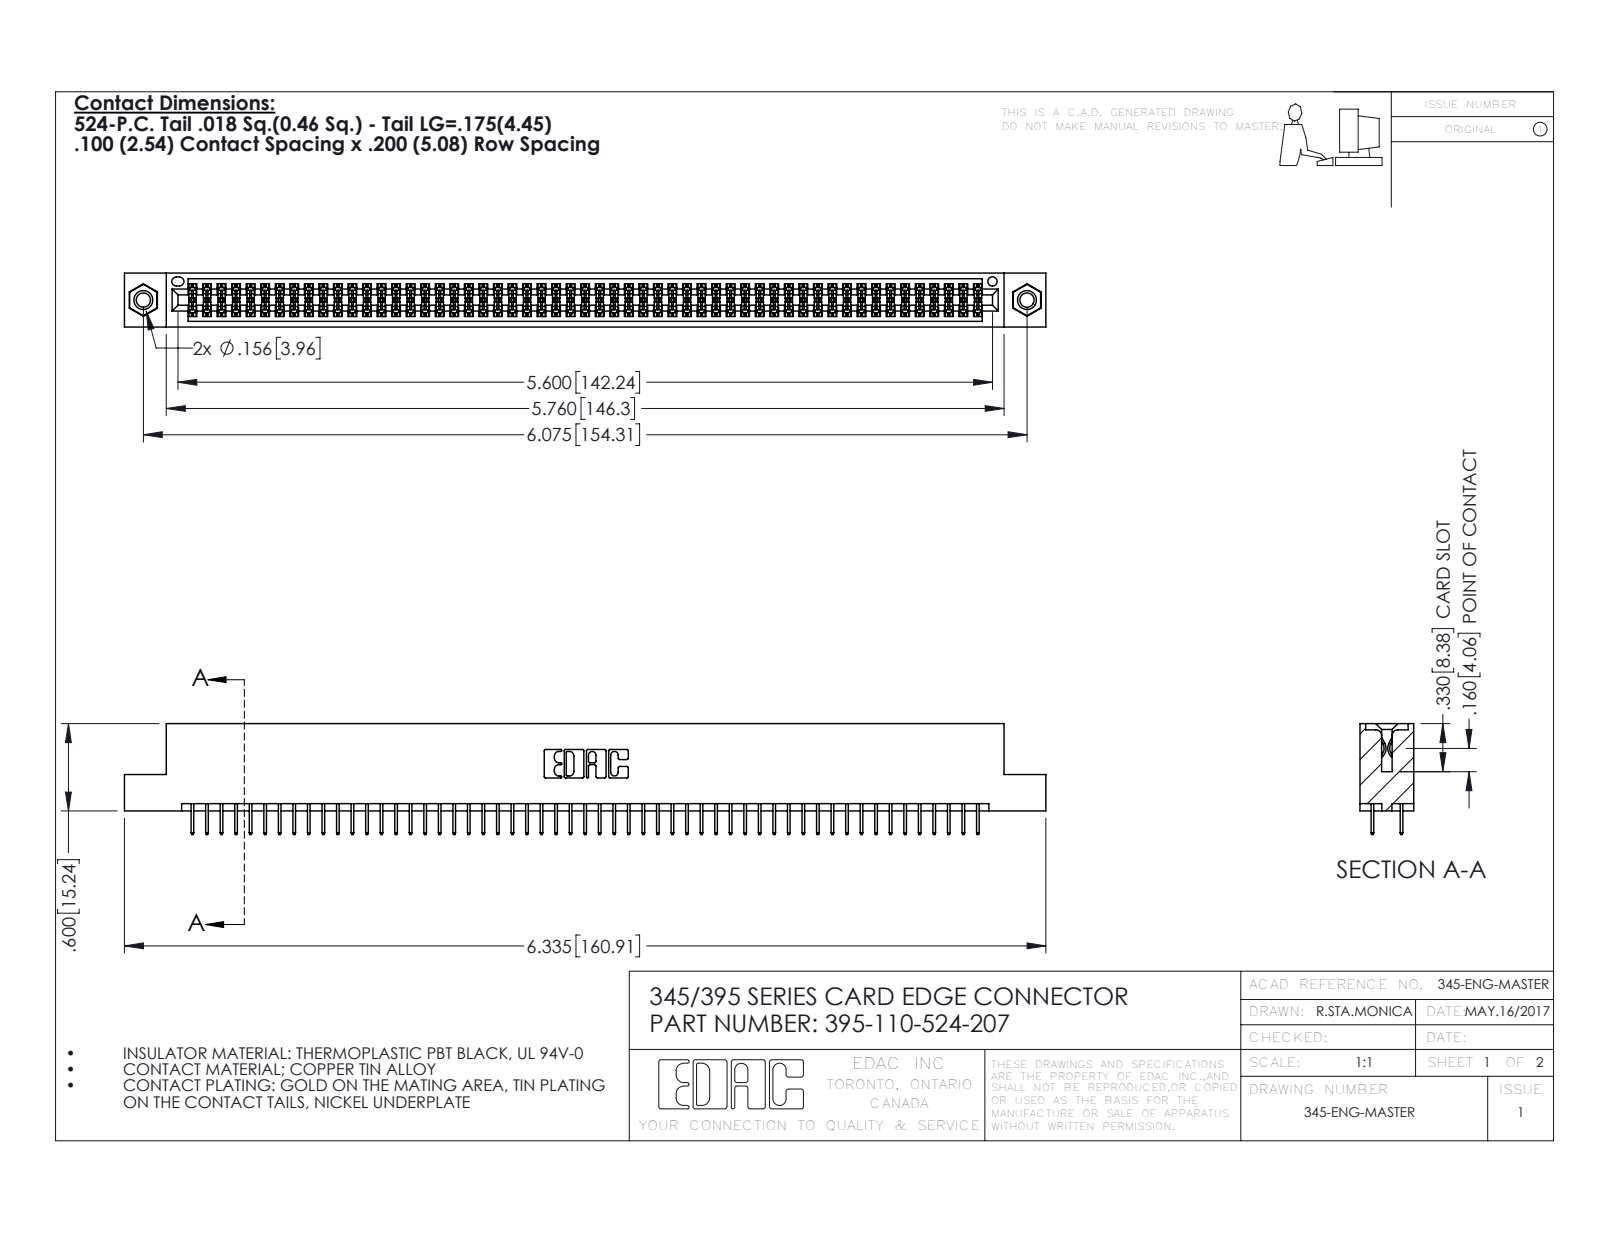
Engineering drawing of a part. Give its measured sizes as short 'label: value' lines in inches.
name: 345-292-001_345-293-124; 345-250-001_345-250-005-103; 345 Part_Flush Mounting Lugs - 0.156 Dia-TI; 395-110-524-207
written by: SolidWorks 2016 (CONFIG_CONTROL_DESIGN)
unit: in
bodies: 113 solids, 6126 faces (4402 planar, 1708 cylindrical, 16 other)
size: 6.335 × 0.762 × 0.37
volume: 0.95 in³; area: 35.43 in²
holes: 2× ⌀0.098, 2× ⌀0.125, 2× ⌀0.156, 1× ⌀0.064
bosses: 2× ⌀0.155
rounds: 165× R0.006, 22× R0.01, 6× R0.007, 6× R0.031, 3× R0.026, 2× R0.014, 2× R0.019, 2× R0.022
face distances: 0.072, 0.298, 0.2, 0.37, 0.098, 0.272, 0.025, 0.225, 0.072, 0.175
hole spacings: 0.27, 5.839, 6.075
